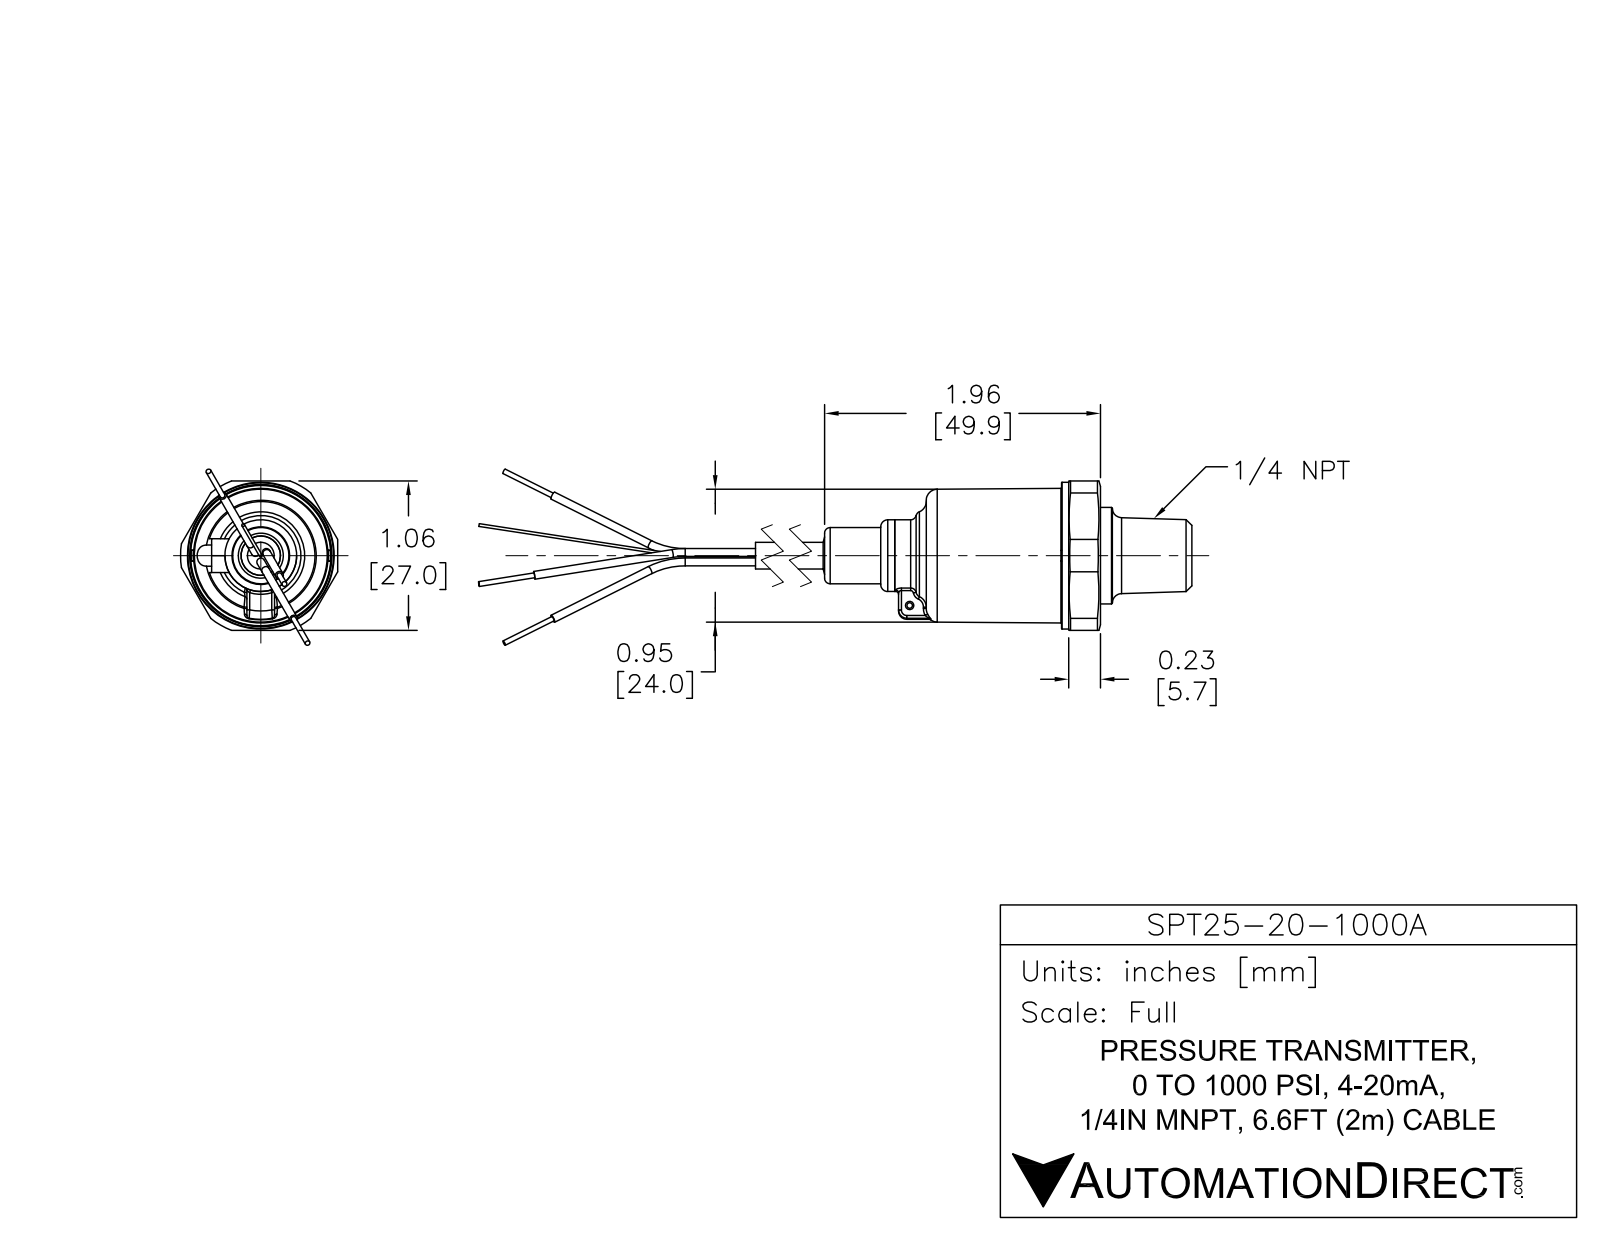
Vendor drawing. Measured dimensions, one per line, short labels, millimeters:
name: SPT25-20-1000A
written by: SolidWorks 2017 (AUTOMOTIVE_DESIGN)
unit: mm
bodies: 7 solids, 116 faces (32 planar, 49 cylindrical, 35 other)
size: 153.3 × 29 × 27.09
volume: 20 801 mm³; area: 7 170 mm²
holes: 1× ⌀1, 1× ⌀3.3
bosses: 6× ⌀1.4, 5× ⌀0.75, 1× ⌀26.75, 1× ⌀24, 1× ⌀17.5, 1× ⌀14, 1× ⌀13, 1× ⌀10
rounds: 1× R2, 1× R14.5
face distances: 6.75, 24, 17.25, 42.75, 49.5, 66.75, 44, 1.25, 5.5, 22.75
